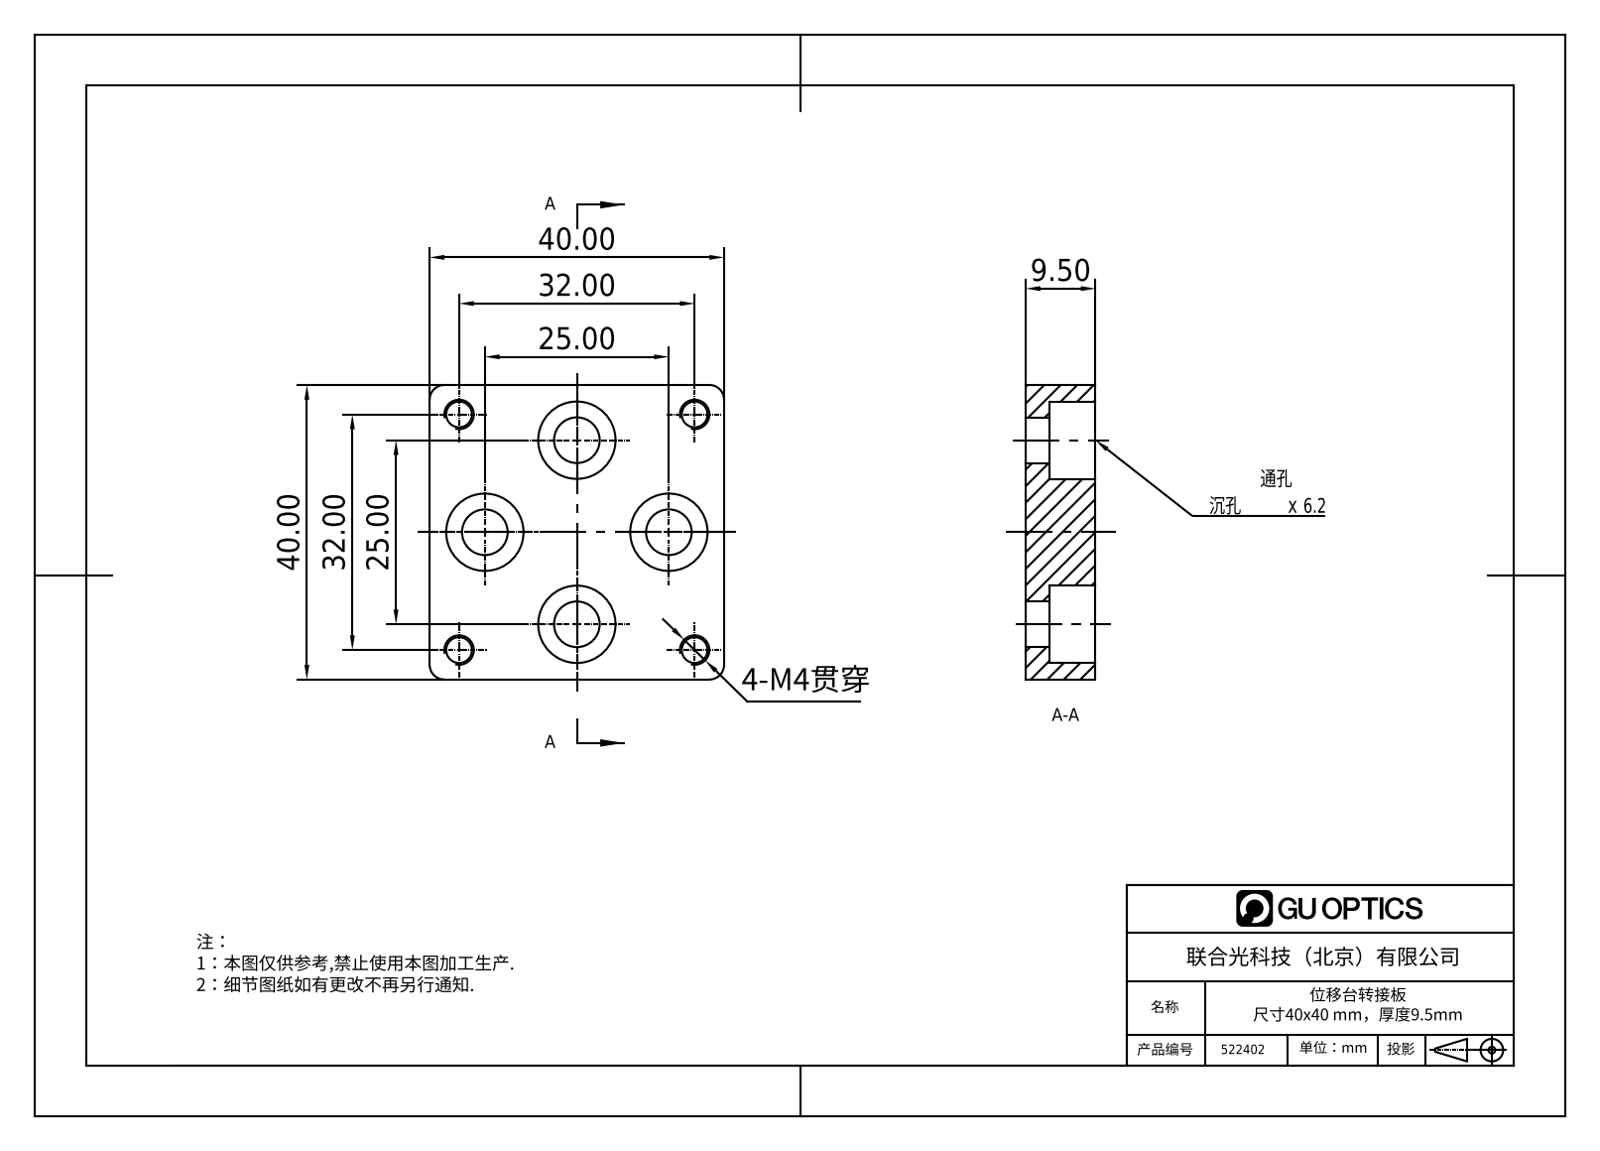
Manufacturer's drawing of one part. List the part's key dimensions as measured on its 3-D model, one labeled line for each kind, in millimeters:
Part name (STEP PRODUCT): 516300转接板
STEP written by: SolidWorks 2020 (CONFIG_CONTROL_DESIGN)
Units: millimetres
Bodies: 1 solid, 26 faces (10 planar, 16 cylindrical, 0 other)
Overall size (bounding box): 40 × 40 × 9.5
Volume: 12 256 mm³ · Surface area: 5 855 mm²
Round holes (diameter × count): ⌀3.5 ×4, ⌀6.2 ×4, ⌀10.5 ×4
Partial cylindrical surfaces — rounded edges, fillets, slot ends (radius × count): R2 ×4
Main face-to-face distances: 9.5, 40, 3.3, 6.2
Hole centre spacings: 16.38, 32.68, 17.68, 32, 25, 45.25
